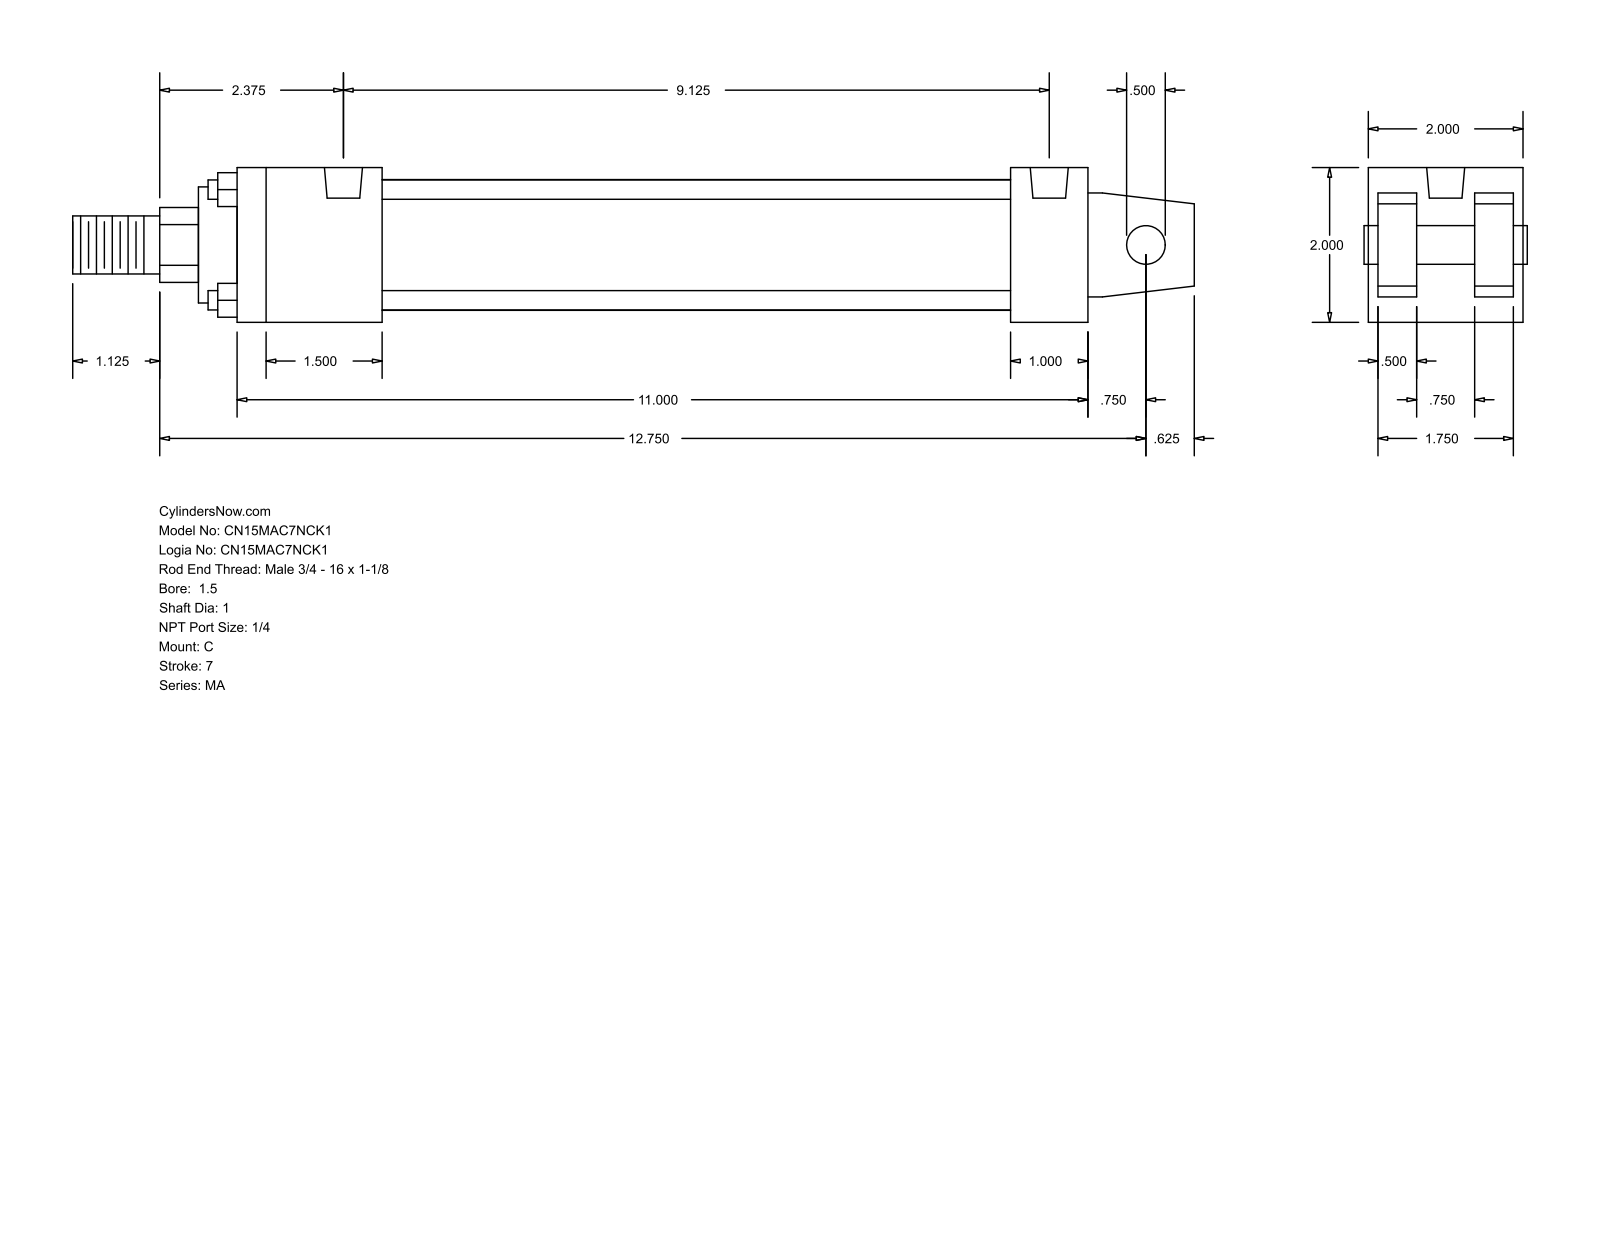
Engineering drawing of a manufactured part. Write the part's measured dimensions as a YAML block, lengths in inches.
part_name: "MA_C__0150_1"
step_written_by: "GSSL Pune (CONFIG_CONTROL_DESIGN)"
units: inches
bodies: {solids: 0, faces: 103, planar: 76, cylindrical: 27, other: 0}
overall_size: [14.5, 2, 2]
round_holes:
  - {diameter: 0.313, count: 4}
  - {diameter: 0.492, count: 2}
round_bosses_or_shafts:
  - {diameter: 0.25, count: 4}
  - {diameter: 1.69, count: 1}
  - {diameter: 1.5, count: 1}
  - {diameter: 1, count: 1}
  - {diameter: 0.75, count: 1}
  - {diameter: 0.5, count: 1}
partial_cylinders:
  - {radius: 0.484, count: 1}
face_to_face_distances: [2, 1.875, 0.5, 1.375, 0.125, 0.625, 1.25, 2.375, 10.5, 11]
hole_center_spacings: [9.125]
